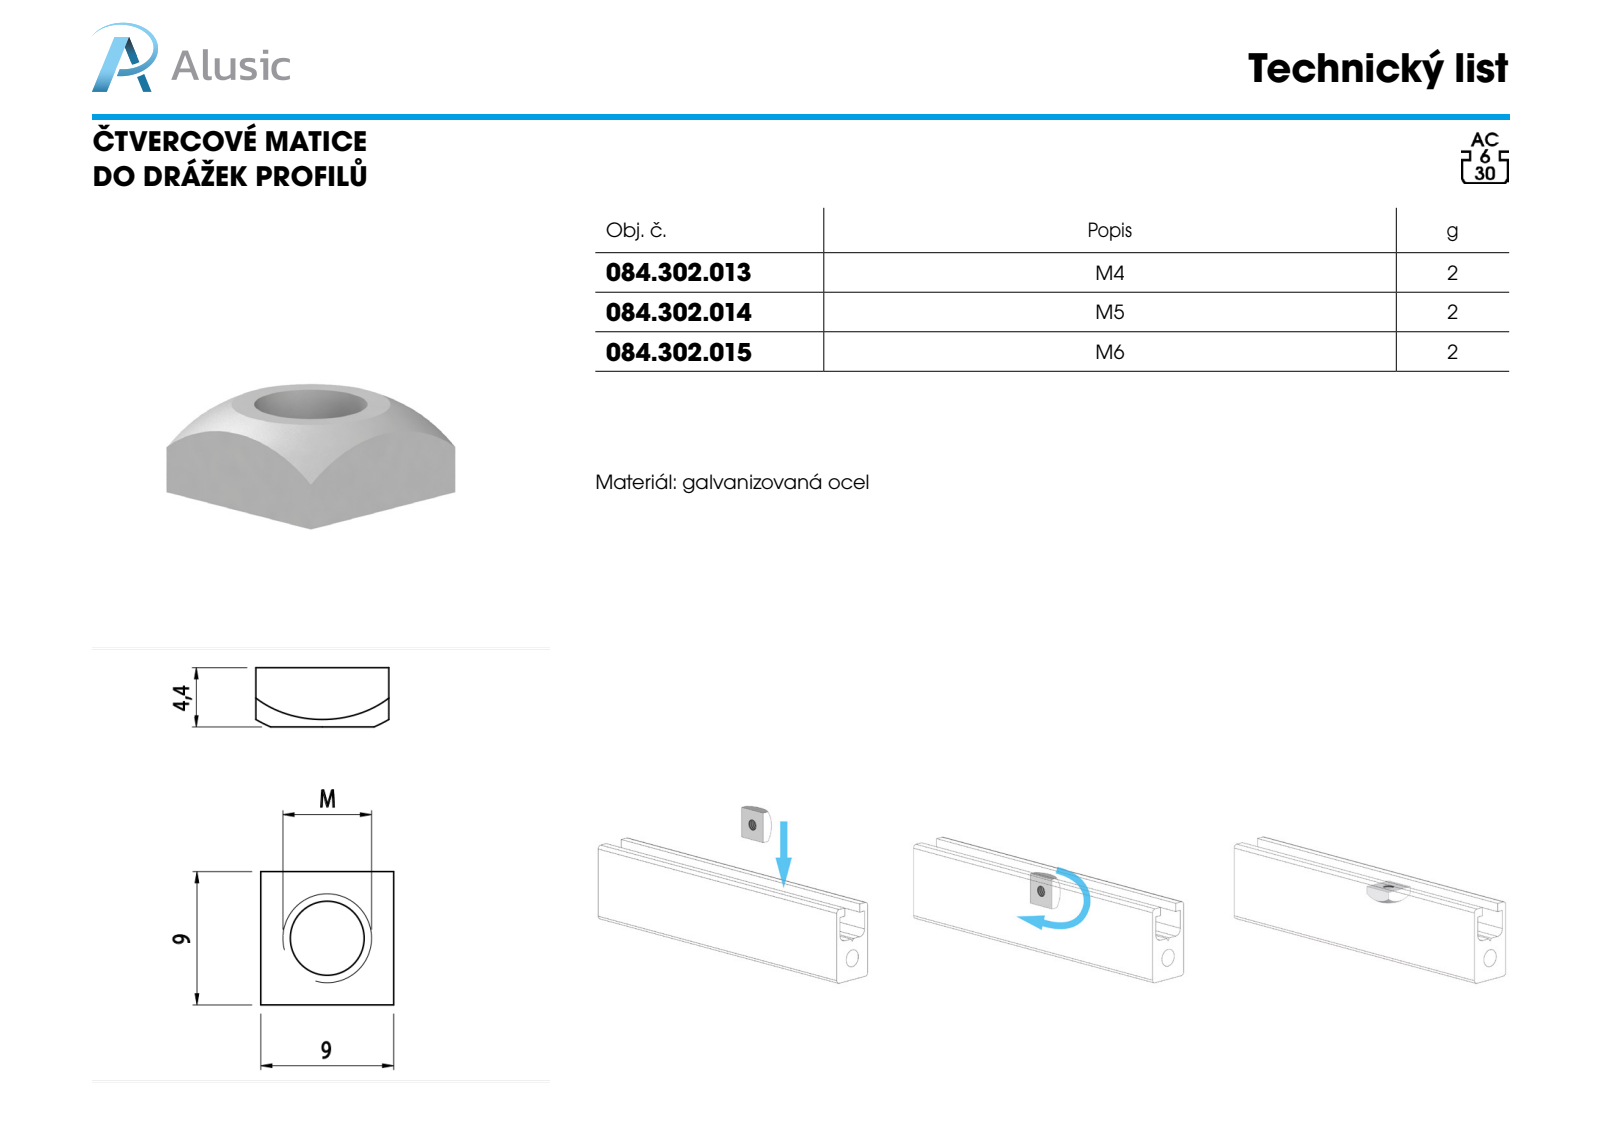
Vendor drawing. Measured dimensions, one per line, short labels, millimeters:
name: 084.302.013
written by: SolidWorks 2012 (CONFIG_CONTROL_DESIGN)
unit: mm
bodies: 1 solid, 10 faces (6 planar, 2 cylindrical, 2 other)
size: 9 × 9 × 4
volume: 268 mm³; area: 303 mm²
holes: 1× ⌀3.3
face distances: 9, 4
